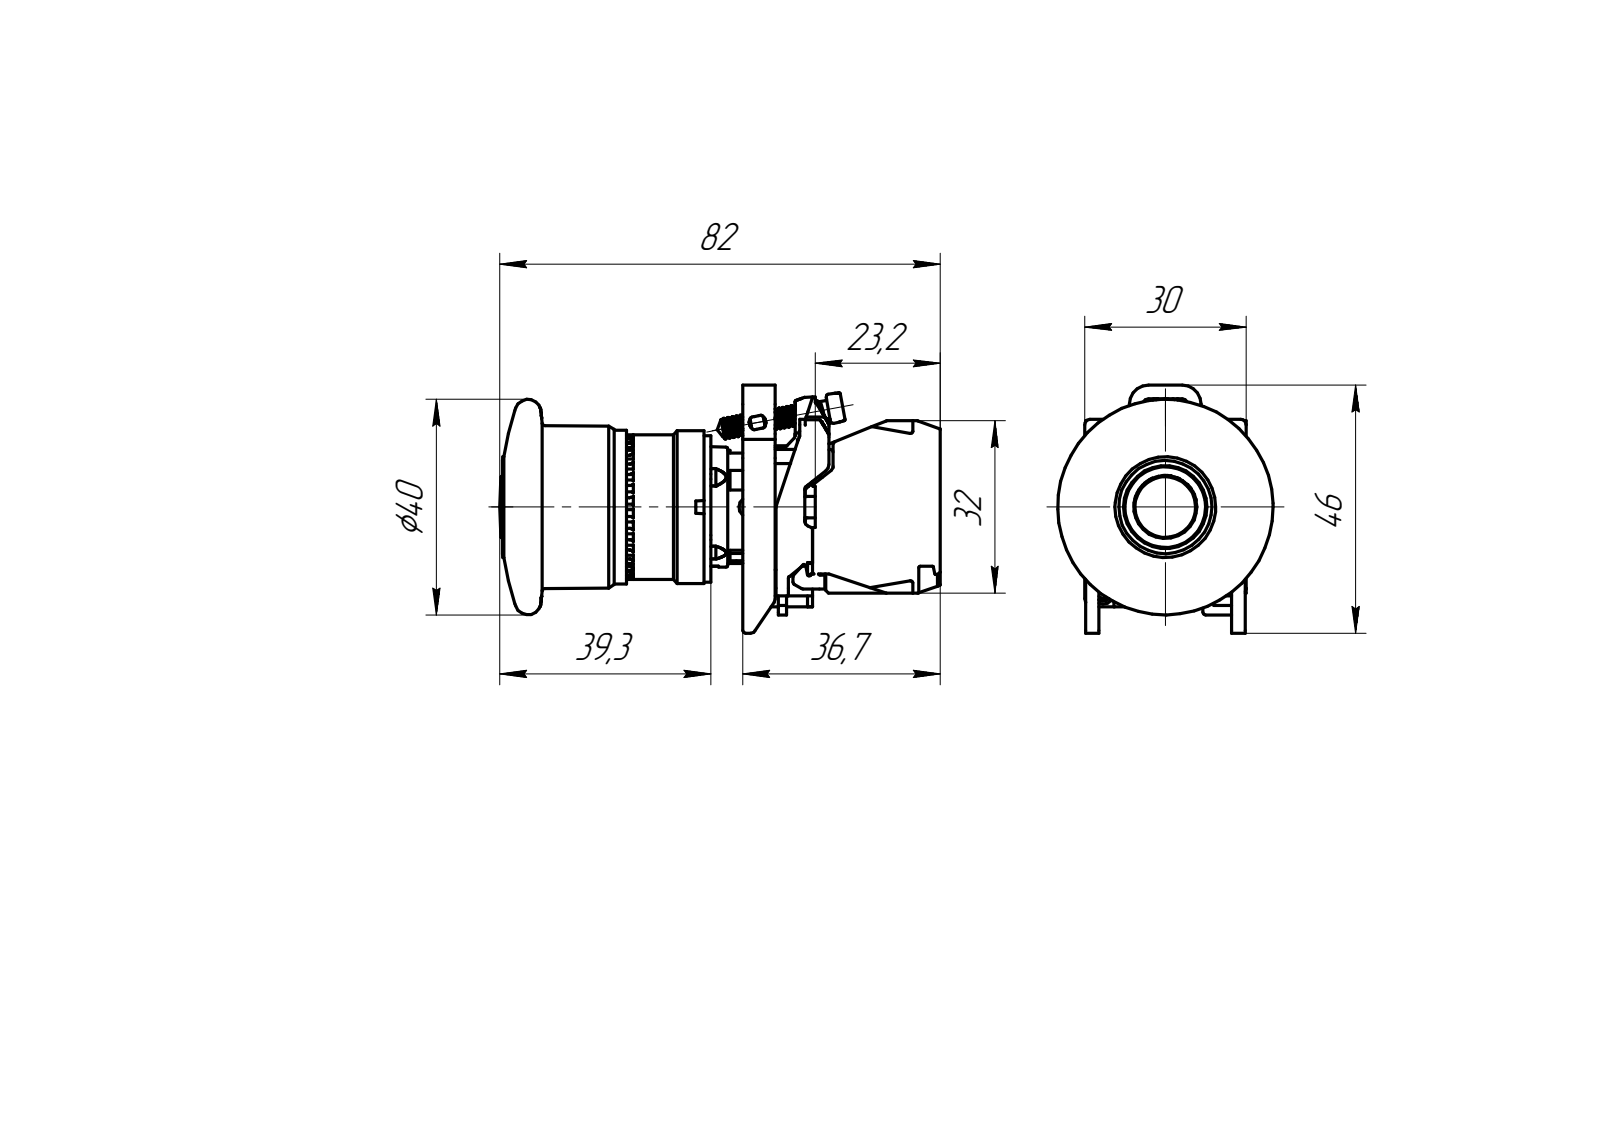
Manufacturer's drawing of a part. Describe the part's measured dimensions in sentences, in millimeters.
The part is named "ZB4BE009; ZBE101; ZBE102; ZB4BT4C (+1 more)". Its 3-D file was written by "PRO/ENGINEER BY PARAMETRIC TECHNOLOGY CORPORATION, 2010280 (AUTOMOTIVE_DESIGN)". It is 25 solids with 5253 faces: 3083 planar, 1435 cylindrical and 735 other. Overall it measures 81.85 by 46 by 40 millimeters. Its volume is 48 891 cubic millimeters and its surface area 26 175 square millimeters. Round holes: 9 of diameter 2.5, 4 of diameter 1.9, 4 of diameter 2.6, 4 of diameter 2.9, 4 of diameter 4, 1 of diameter 1.5, 1 of diameter 3.8, 1 of diameter 5.2, 1 of diameter 9.2, 1 of diameter 17.3. Round bosses or shafts: 4 of diameter 5.6, 4 of diameter 2.9, 4 of diameter 2.7, 4 of diameter 2.4, 1 of diameter 28.51, 1 of diameter 28.4, 1 of diameter 26.8, 1 of diameter 21. Partial cylindrical surfaces (rounded edges, fillets, slot ends): 273 of radius 0.2, 120 of radius 0.1, 77 of radius 0.3, 62 of radius 0.15, 57 of radius 0.5, 42 of radius 1, 13 of radius 0.4, 11 of radius 2. The main face-to-face distances are 20, 9.8, 1, 29.8, 2.5, 6, 0.5, 1.4, 1.3, 1.5. The hole center spacings are 20, 4, 5.9, 6.09, 10.96, 11.82, 12.21, 13.65.
